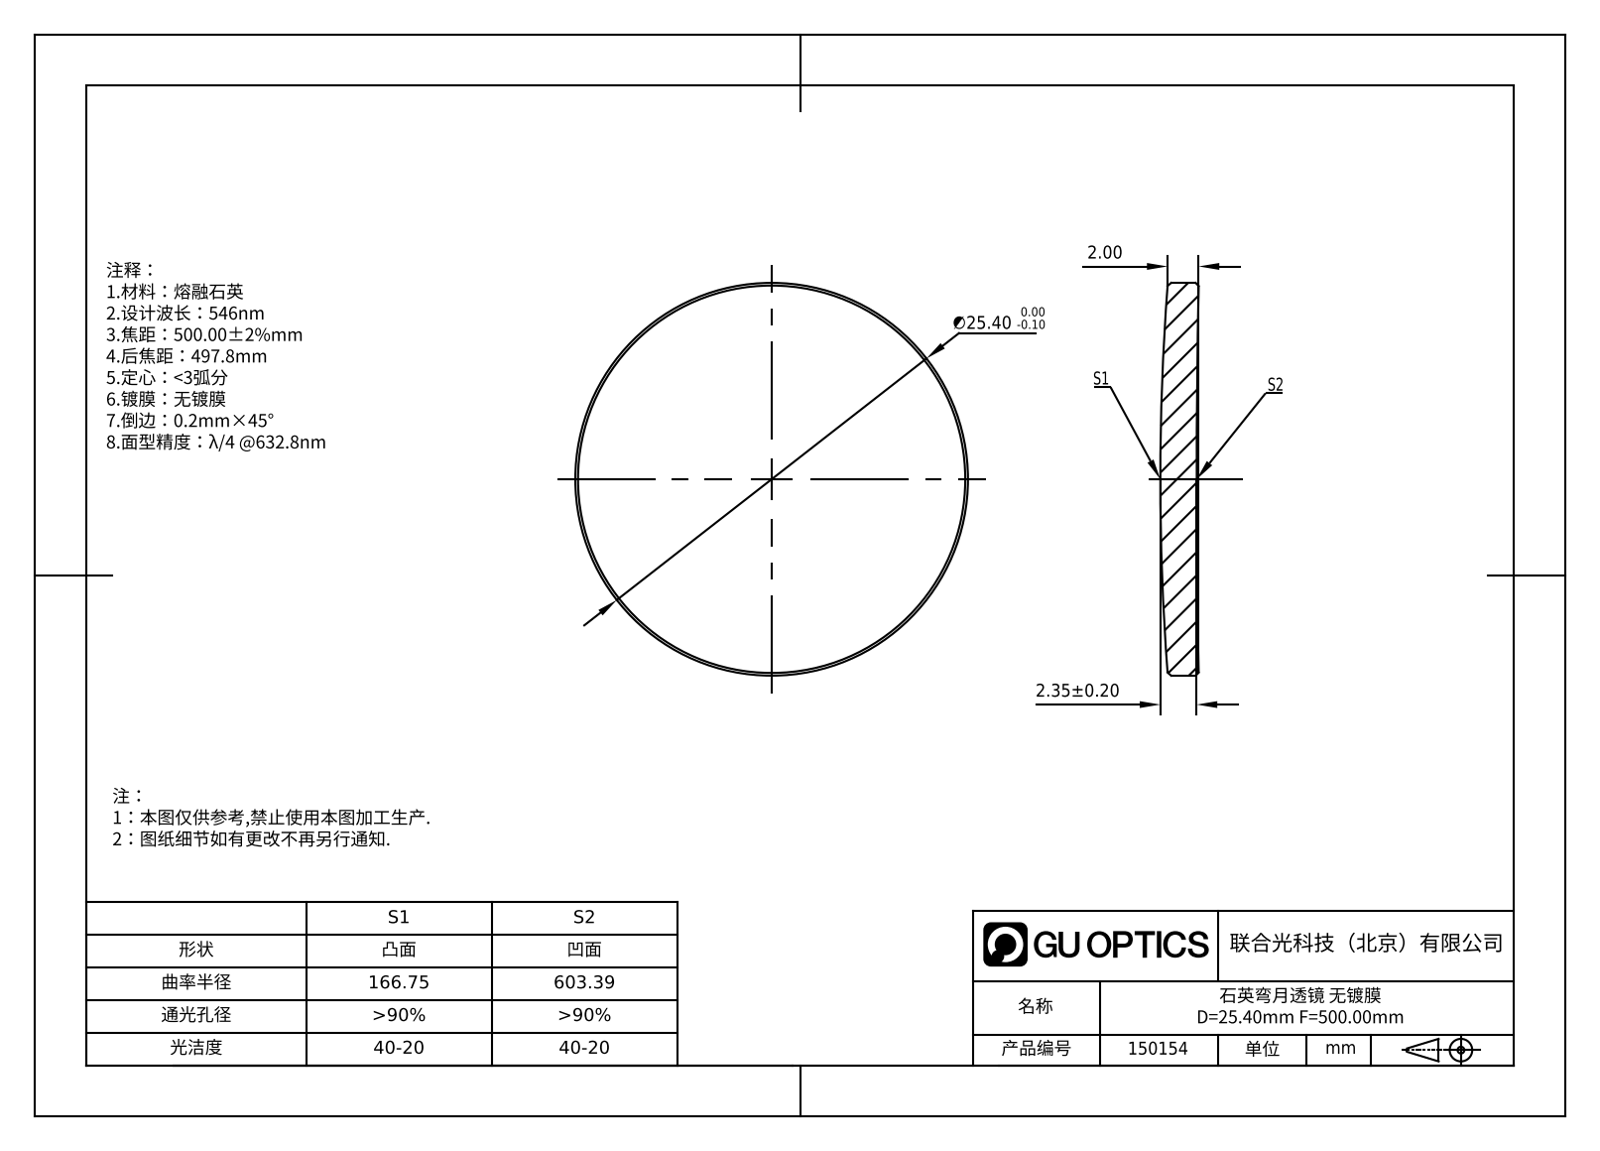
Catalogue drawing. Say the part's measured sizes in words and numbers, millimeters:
The part is named "GLM2-025B-500". Its 3-D file was written by "SolidWorks 2022 (AUTOMOTIVE_DESIGN)". It is 1 solid with 10 faces: 0 planar, 2 cylindrical and 8 other. Overall it measures 25.4 by 25.4 by 2.48 millimeters. Its volume is 1 099 cubic millimeters and its surface area 1 155 square millimeters. Round bosses or shafts: 1 of diameter 25.4.
